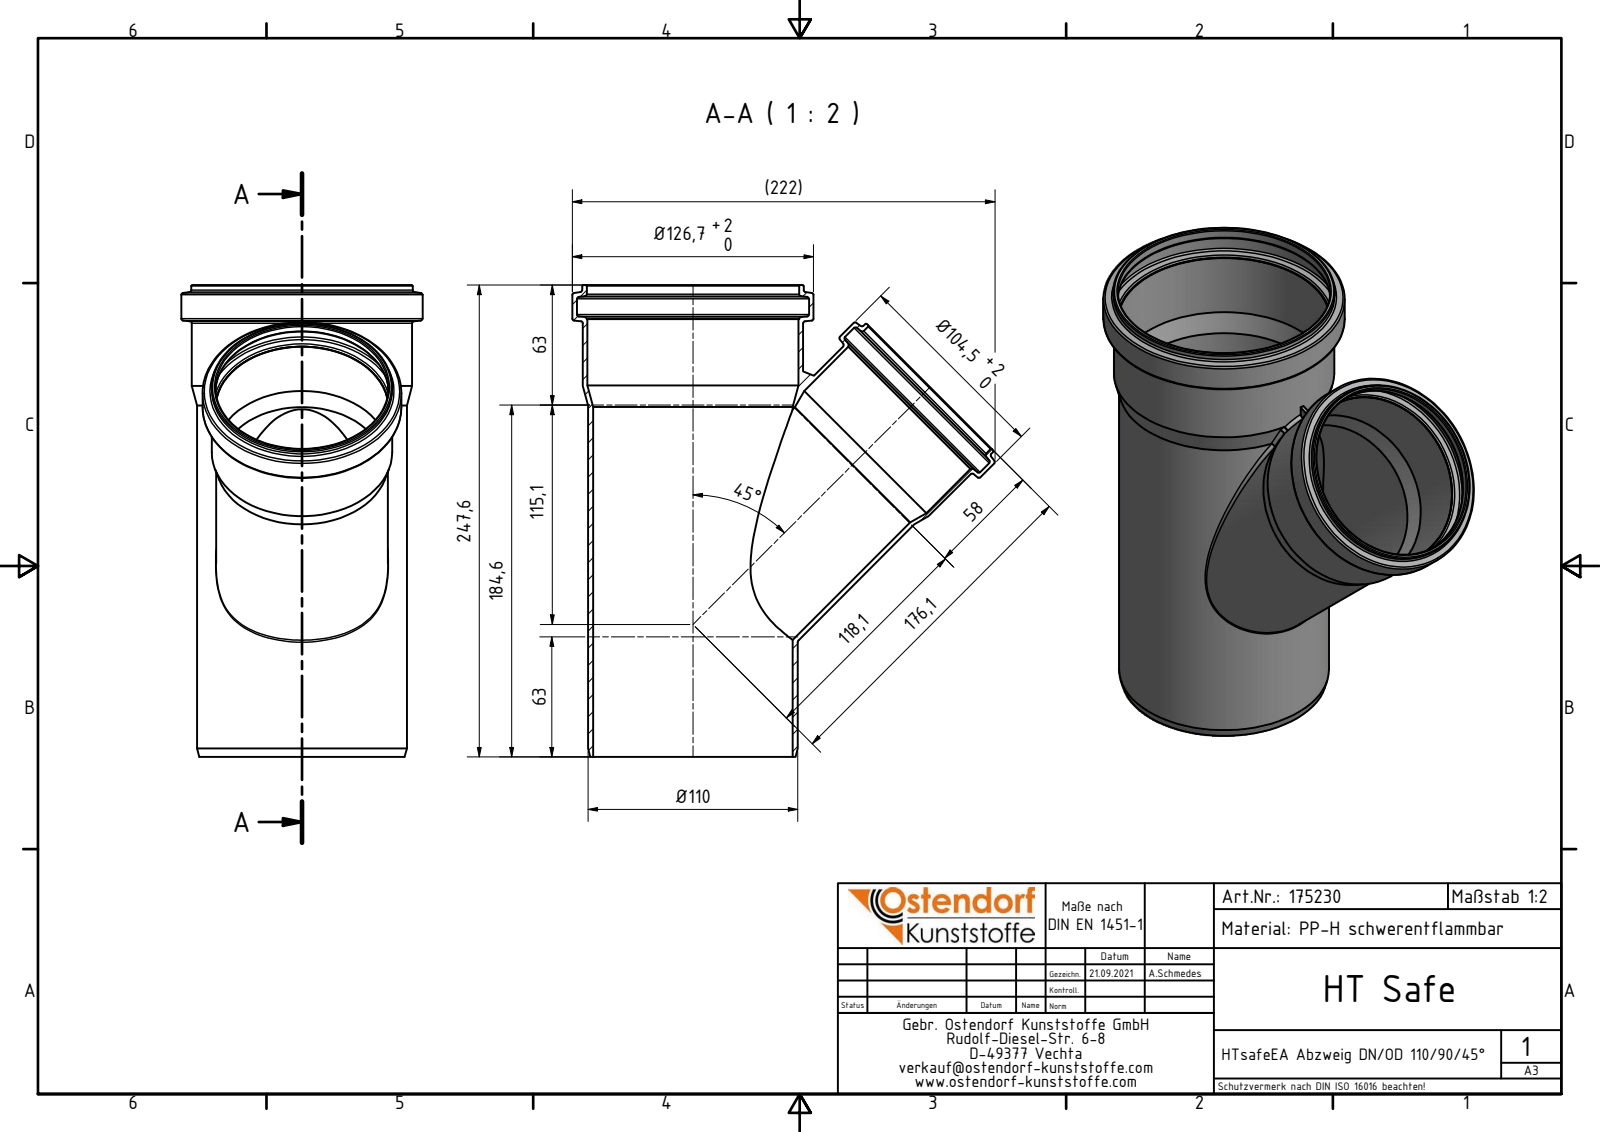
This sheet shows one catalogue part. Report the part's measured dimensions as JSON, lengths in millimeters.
{"part_name": "175230 HTsafeEA DN_OD 110_90_45°", "step_written_by": "Autodesk Inventor 2020 (AUTOMOTIVE_DESIGN)", "units": "millimeters", "bodies": {"solids": 1, "faces": 68, "planar": 8, "cylindrical": 18, "other": 42}, "overall_size": [247.6, 221.96, 126.7], "volume_mm3": 281153, "surface_area_mm2": 229180, "round_holes": [[90.9, 2], [85.6, 1], [90.7, 1], [100.4, 1], [104.8, 1], [110.9, 1], [111.5, 1], [121.9, 1]], "round_bosses_or_shafts": [[126.7, 1], [116.3, 1], [115.7, 1], [110.2, 1], [104.4, 1], [94.9, 1], [94.7, 1], [90.2, 1]], "face_to_face_distances": [247.6, 229.77, 17.83, 15.31, 2]}
